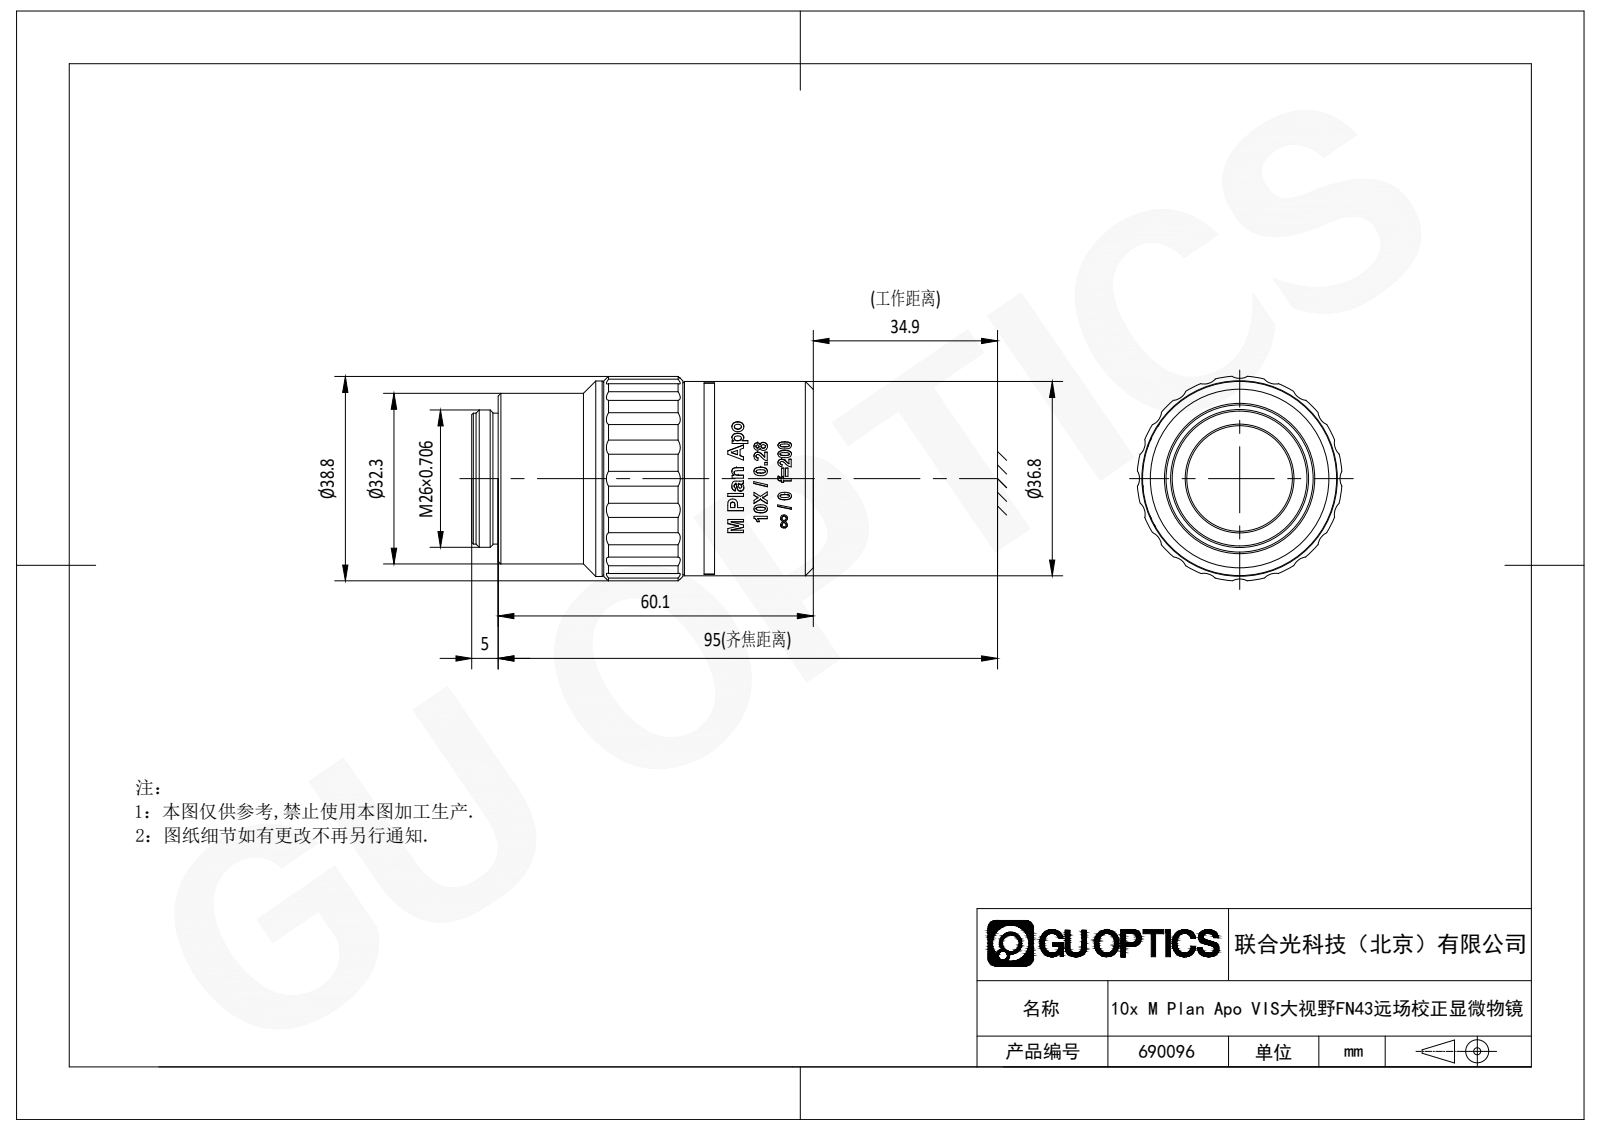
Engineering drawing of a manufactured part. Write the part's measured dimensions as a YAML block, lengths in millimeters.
part_name: "690096; 装饰圈.stp"
step_written_by: "SolidWorks 2020 (AUTOMOTIVE_DESIGN)"
units: millimeters
bodies: {solids: 3, faces: 482, planar: 109, cylindrical: 122, other: 251}
overall_size: [64.7, 38.7, 38.7]
volume: 21259
surface_area: 23693
round_holes:
  - {diameter: 20, count: 1}
  - {diameter: 22, count: 1}
  - {diameter: 22.9, count: 1}
  - {diameter: 27.9, count: 1}
  - {diameter: 29, count: 1}
  - {diameter: 30, count: 1}
  - {diameter: 30.5, count: 1}
  - {diameter: 31.4, count: 1}
  - {diameter: 34.8, count: 1}
round_bosses_or_shafts:
  - {diameter: 37, count: 1}
  - {diameter: 36.8, count: 1}
  - {diameter: 35.3, count: 1}
  - {diameter: 34.5, count: 1}
  - {diameter: 34.2, count: 1}
  - {diameter: 32.3, count: 1}
  - {diameter: 26, count: 1}
  - {diameter: 24.8, count: 1}
partial_cylinders:
  - {radius: 3, count: 20}
  - {radius: 18.3, count: 1}
  - {radius: 19.4, count: 1}
face_to_face_distances: [59.7, 1, 39.7, 18.3, 2, 57, 58.7, 38.7, 33.3, 20]
